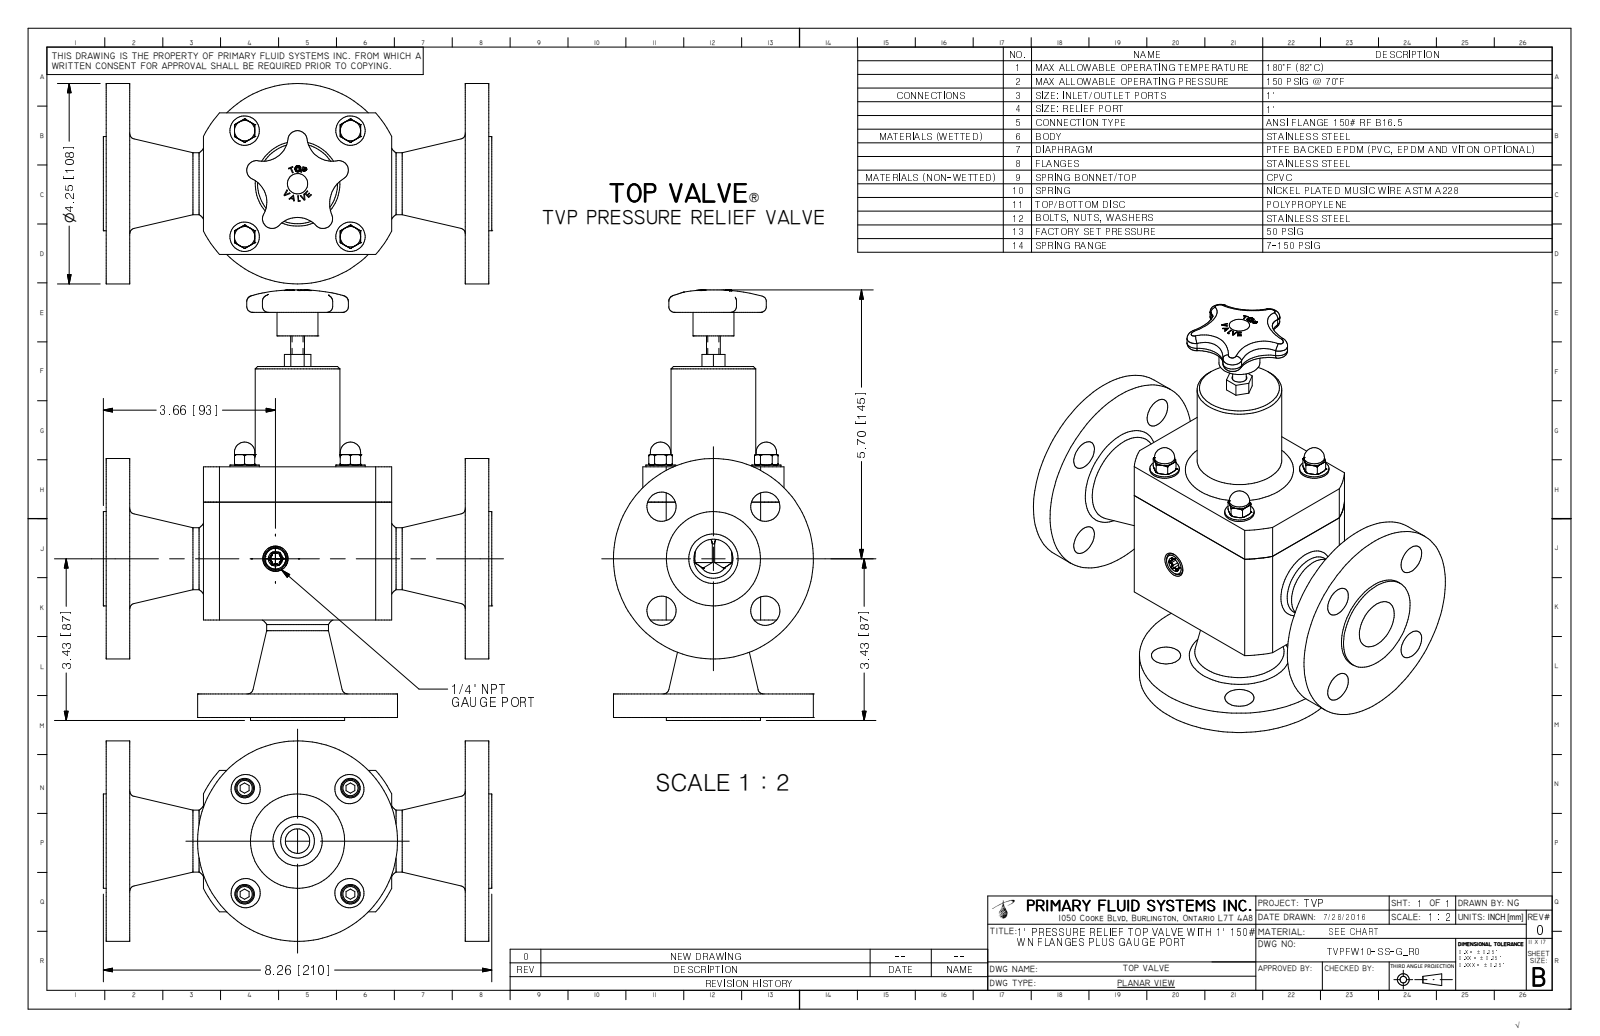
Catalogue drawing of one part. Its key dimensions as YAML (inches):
part_name: "TVPFW10-SS-G_R0"
step_written_by: "Autodesk Inventor 2009 (AUTOMOTIVE_DESIGN)"
units: inches
bodies: {solids: 1, faces: 402, planar: 164, cylindrical: 75, other: 163}
overall_size: [9.13, 8.26, 4.25]
volume: 68.8
surface_area: 237.5
round_holes:
  - {diameter: 0.62, count: 8}
  - {diameter: 0.175, count: 4}
  - {diameter: 1.049, count: 2}
  - {diameter: 2.525, count: 1}
round_bosses_or_shafts:
  - {diameter: 0.625, count: 4}
  - {diameter: 0.433, count: 4}
  - {diameter: 0.375, count: 4}
  - {diameter: 4.25, count: 2}
  - {diameter: 2, count: 2}
  - {diameter: 1.315, count: 2}
  - {diameter: 2.5, count: 1}
  - {diameter: 1.8, count: 1}
partial_cylinders:
  - {radius: 0.027, count: 6}
  - {radius: 0.085, count: 5}
  - {radius: 0.205, count: 5}
  - {radius: 0.536, count: 4}
  - {radius: 0.656, count: 4}
  - {radius: 0.625, count: 1}
  - {radius: 0.745, count: 1}
  - {radius: 2.238, count: 1}
face_to_face_distances: [0.5, 2.067, 1.567, 7.635, 3, 8.135, 6.067, 5.567, 7.135, 0.063]
hole_center_spacings: [1.56, 2.206, 2.228, 2.228, 2.25, 3.12, 0.031, 3.151]
